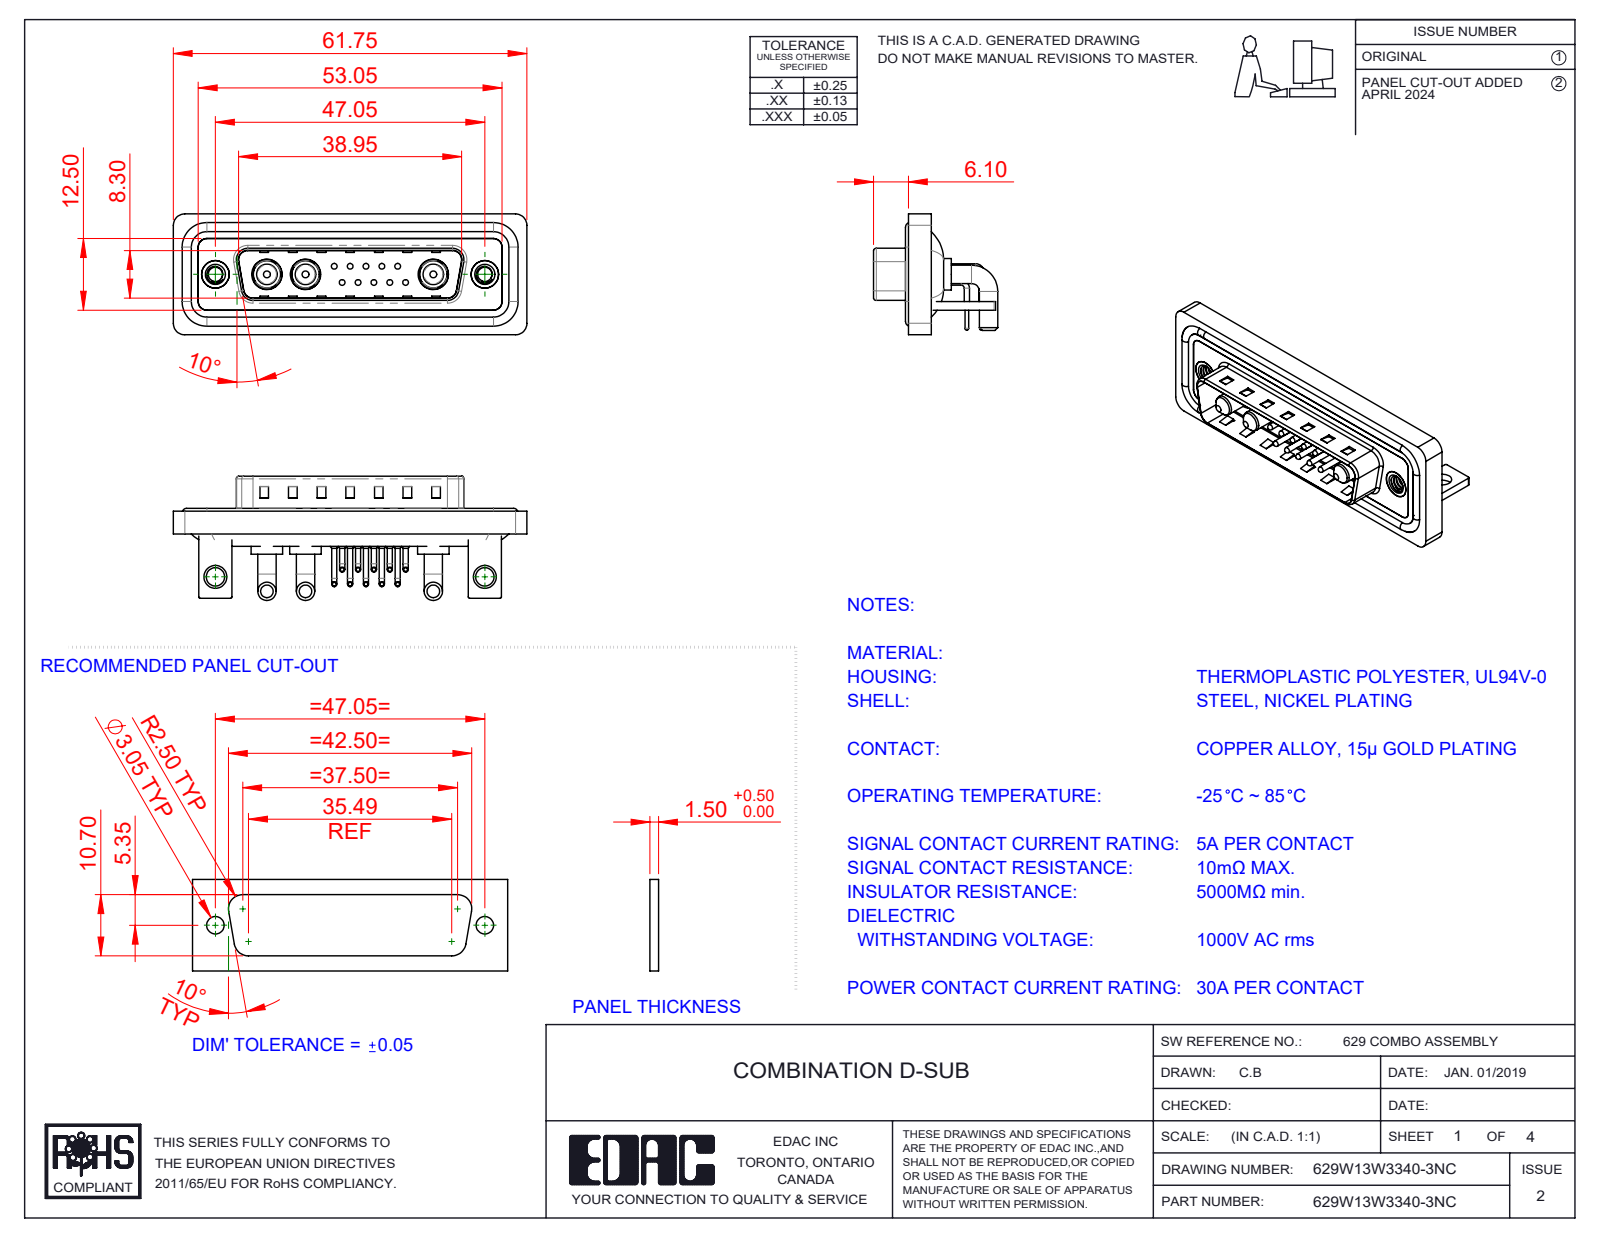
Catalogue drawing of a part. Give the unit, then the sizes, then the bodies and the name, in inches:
Units: inches
Overall size (bounding box): 2.431 × 0.854 × 0.831
Round holes (diameter × count): ⌀0.03 ×10, ⌀0.063 ×10, ⌀0.079 ×10, ⌀0.191 ×3, ⌀0.209 ×3, ⌀0.098 ×2, ⌀0.126 ×2, ⌀0.157 ×2, ⌀0.189 ×2, ⌀0.197 ×2
Round bosses / shafts (diameter × count): ⌀0.035 ×20, ⌀0.059 ×10, ⌀0.039 ×10, ⌀0.026 ×10, ⌀0.126 ×6, ⌀0.063 ×4, ⌀0.217 ×3, ⌀0.205 ×3
Partial cylindrical surfaces — rounded edges, fillets, slot ends (radius × count): R0.079 ×19, R0.059 ×18, R0.01 ×16, R0.04 ×10, R0.02 ×9, R0.063 ×8, R0.024 ×4, R0.026 ×4
Main face-to-face distances: 0.016, 0.031, 0.059, 0.114, 0.083, 0.043, 0.161, 0.063, 0.146, 0.177
Hole centre spacings: 0.124, 0.109, 0.198, 0.218, 0.295, 0.198, 0.327, 0.398
Volume: 0.486 in³ · Surface area: 20.37 in²
Bodies: 25 solids, 1750 faces (899 planar, 629 cylindrical, 222 other)
Part name (STEP PRODUCT): 629Combo Housing_13W3; 629Combo Stabilizer Bracket; 629Combo Shell Rear_25 Contacts; Power Pin_30A RA (+6 more)
STEP written by: SolidWorks 2023 (CONFIG_CONTROL_DESIGN)
